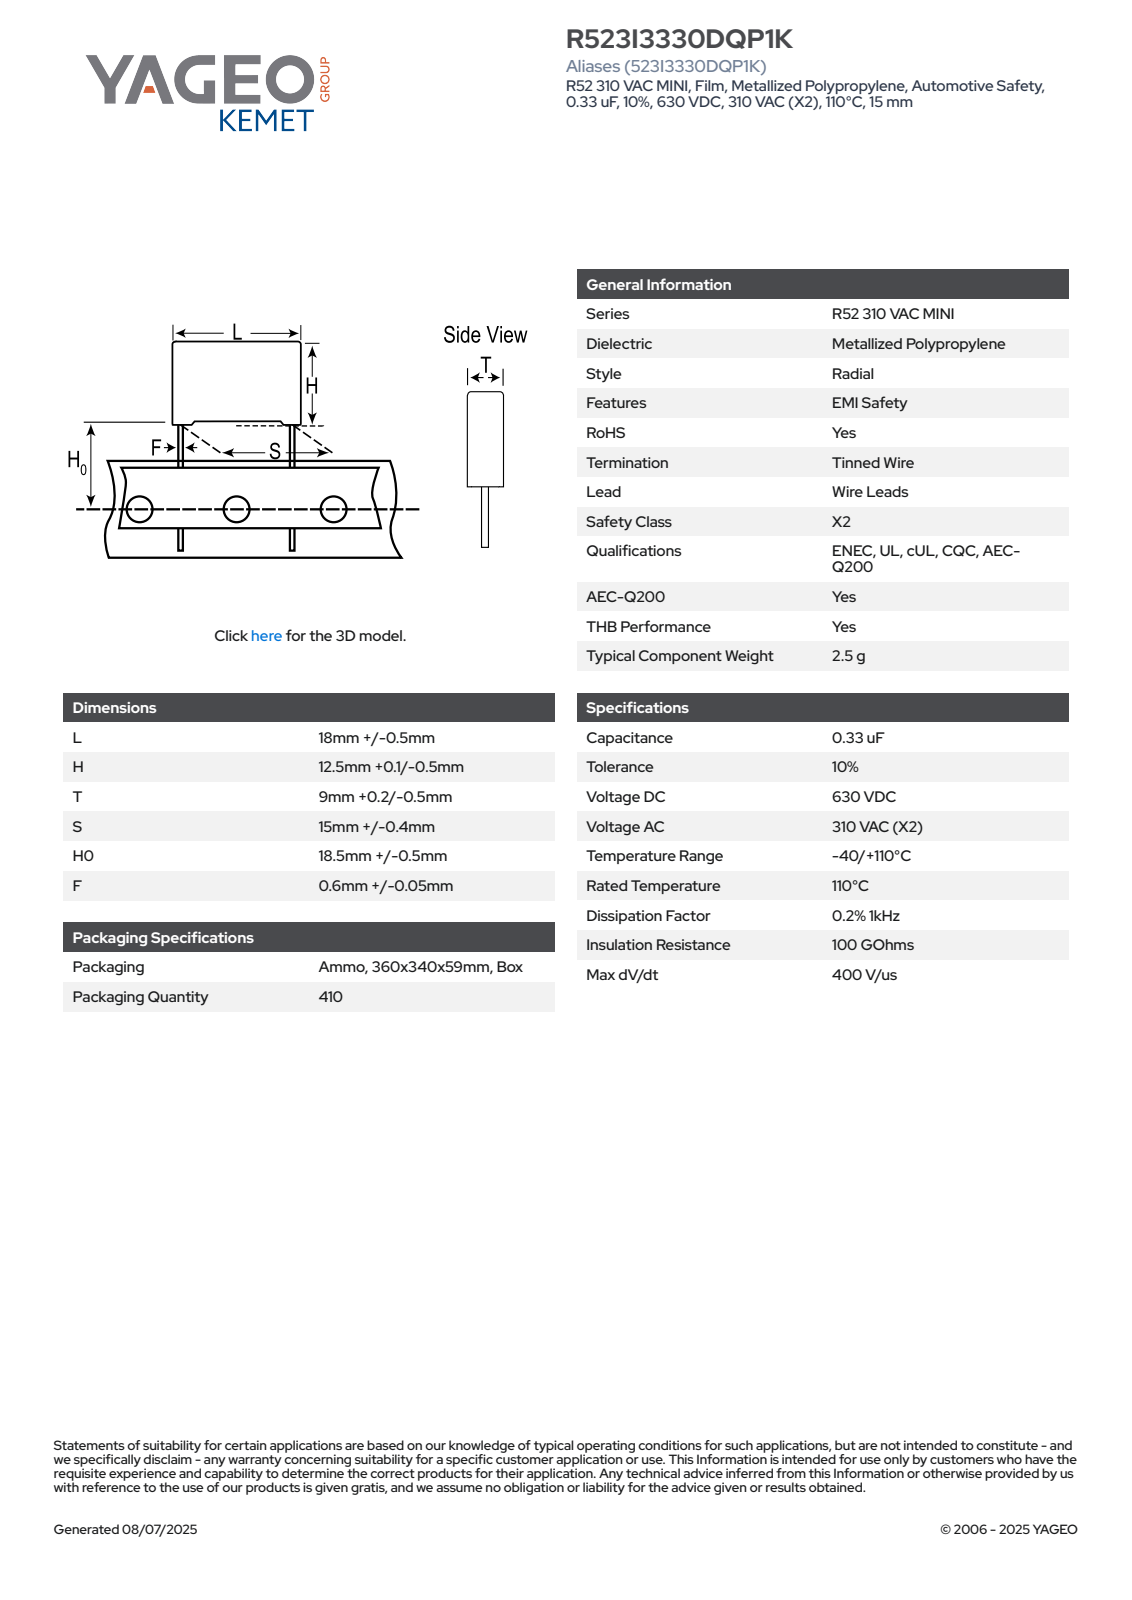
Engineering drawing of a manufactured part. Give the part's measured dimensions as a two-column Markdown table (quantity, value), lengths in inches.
| quantity | value |
| --- | --- |
| part name | CFR_RB2_18X12.5X9_L18.5H12.6T9.2S15H019F0.65 |
| STEP written by | SolidWorks 2020 (AUTOMOTIVE_DESIGN) |
| units | inches |
| bodies | 4 solids, 85 faces (77 planar, 8 cylindrical, 0 other) |
| overall size | 1.244 × 0.728 × 0.363 |
| volume | 0.125 in³ |
| surface area | 1.784 in² |
| round bosses / shafts (diameter × count) | 0.026 × 2 |
| partial cylindrical surfaces (radius × count) | 0.02 × 4 |
| main face-to-face distances | 0.362, 0.467, 0.728, 0.024, 0.03, 0.496, 0.338, 0.017, 0.013, 0.479 |
